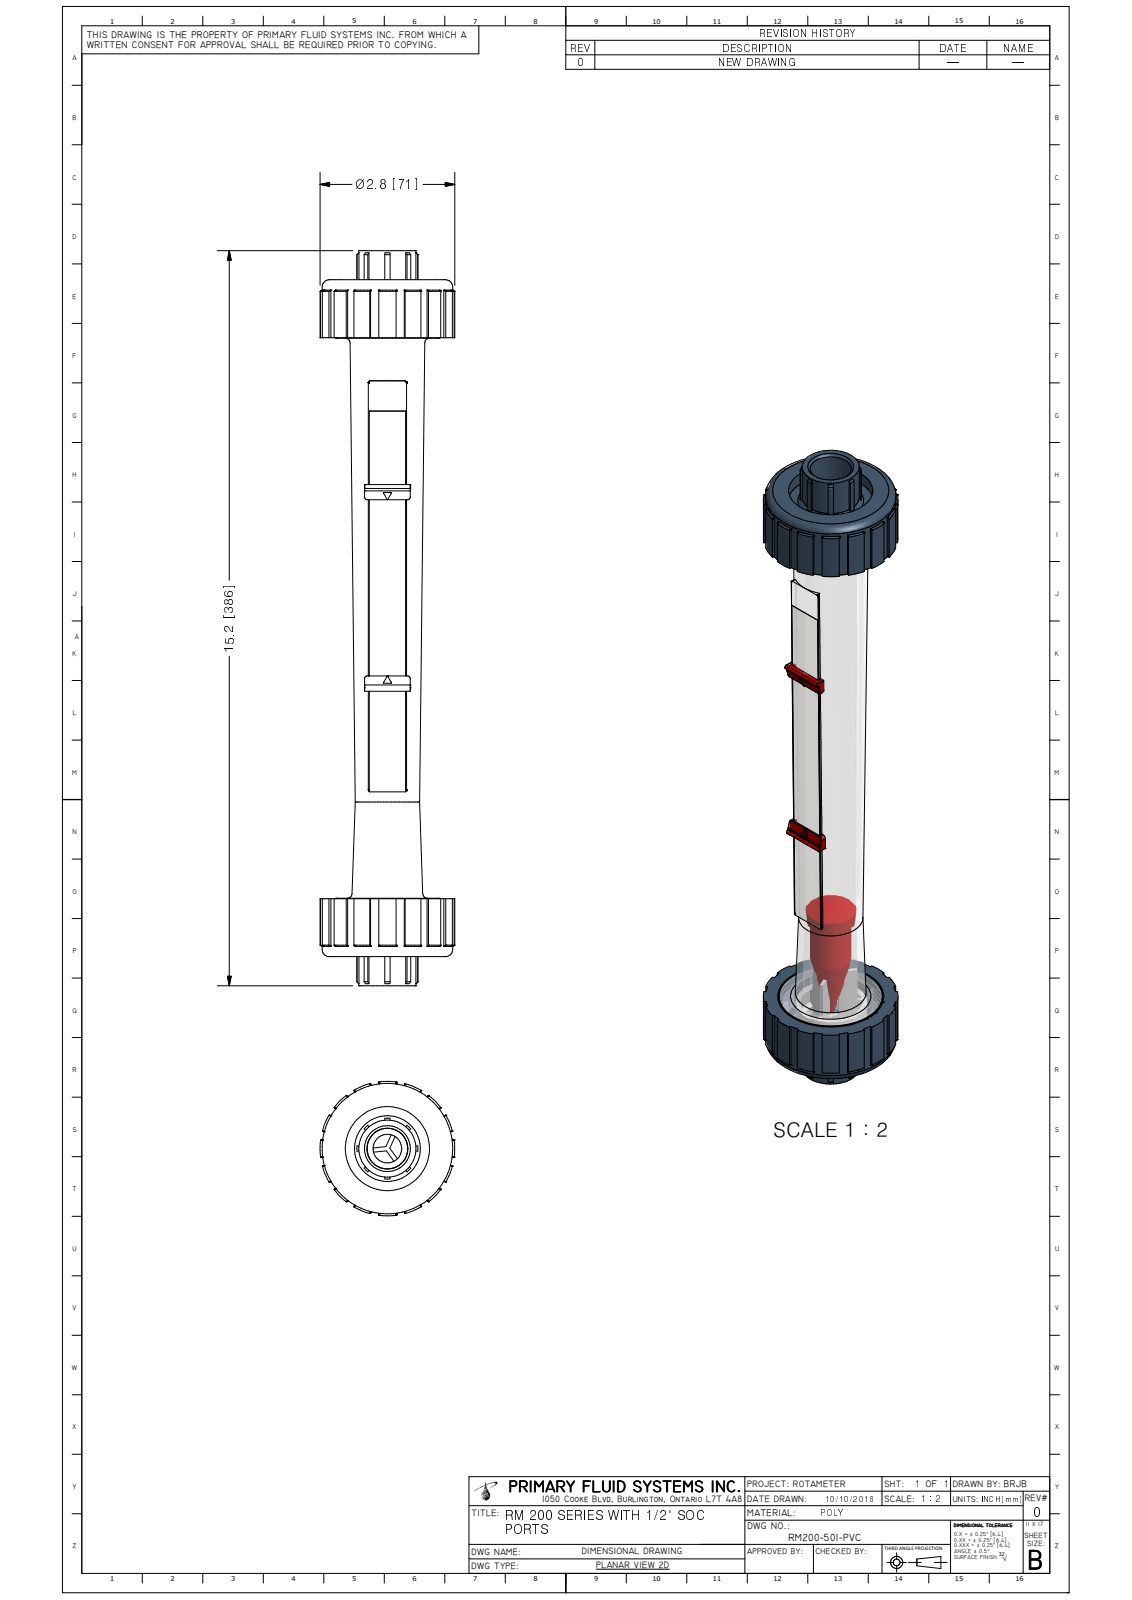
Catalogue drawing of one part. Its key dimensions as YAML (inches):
part_name: "RM200-50I-PVC_R0"
step_written_by: "Autodesk Inventor 2009 (AUTOMOTIVE_DESIGN)"
units: inches
bodies: {solids: 1, faces: 587, planar: 230, cylindrical: 140, other: 217}
overall_size: [15.2, 2.783, 2.783]
volume: 32.1
surface_area: 166
round_holes:
  - {diameter: 1.738, count: 1}
  - {diameter: 2.19, count: 1}
round_bosses_or_shafts:
  - {diameter: 2.697, count: 1}
  - {diameter: 2.152, count: 1}
  - {diameter: 2.03, count: 1}
  - {diameter: 1.485, count: 1}
  - {diameter: 1.18, count: 1}
partial_cylinders:
  - {radius: 0.008, count: 18}
  - {radius: 0.01, count: 16}
  - {radius: 0.004, count: 10}
  - {radius: 0.006, count: 4}
  - {radius: 0.06, count: 4}
  - {radius: 0.008, count: 2}
  - {radius: 0.04, count: 2}
  - {radius: 0.045, count: 2}
face_to_face_distances: [1.197, 12.799, 1.207, 12.789, 11.592, 0.498, 13.498, 0.699, 12.301, 0.256]
